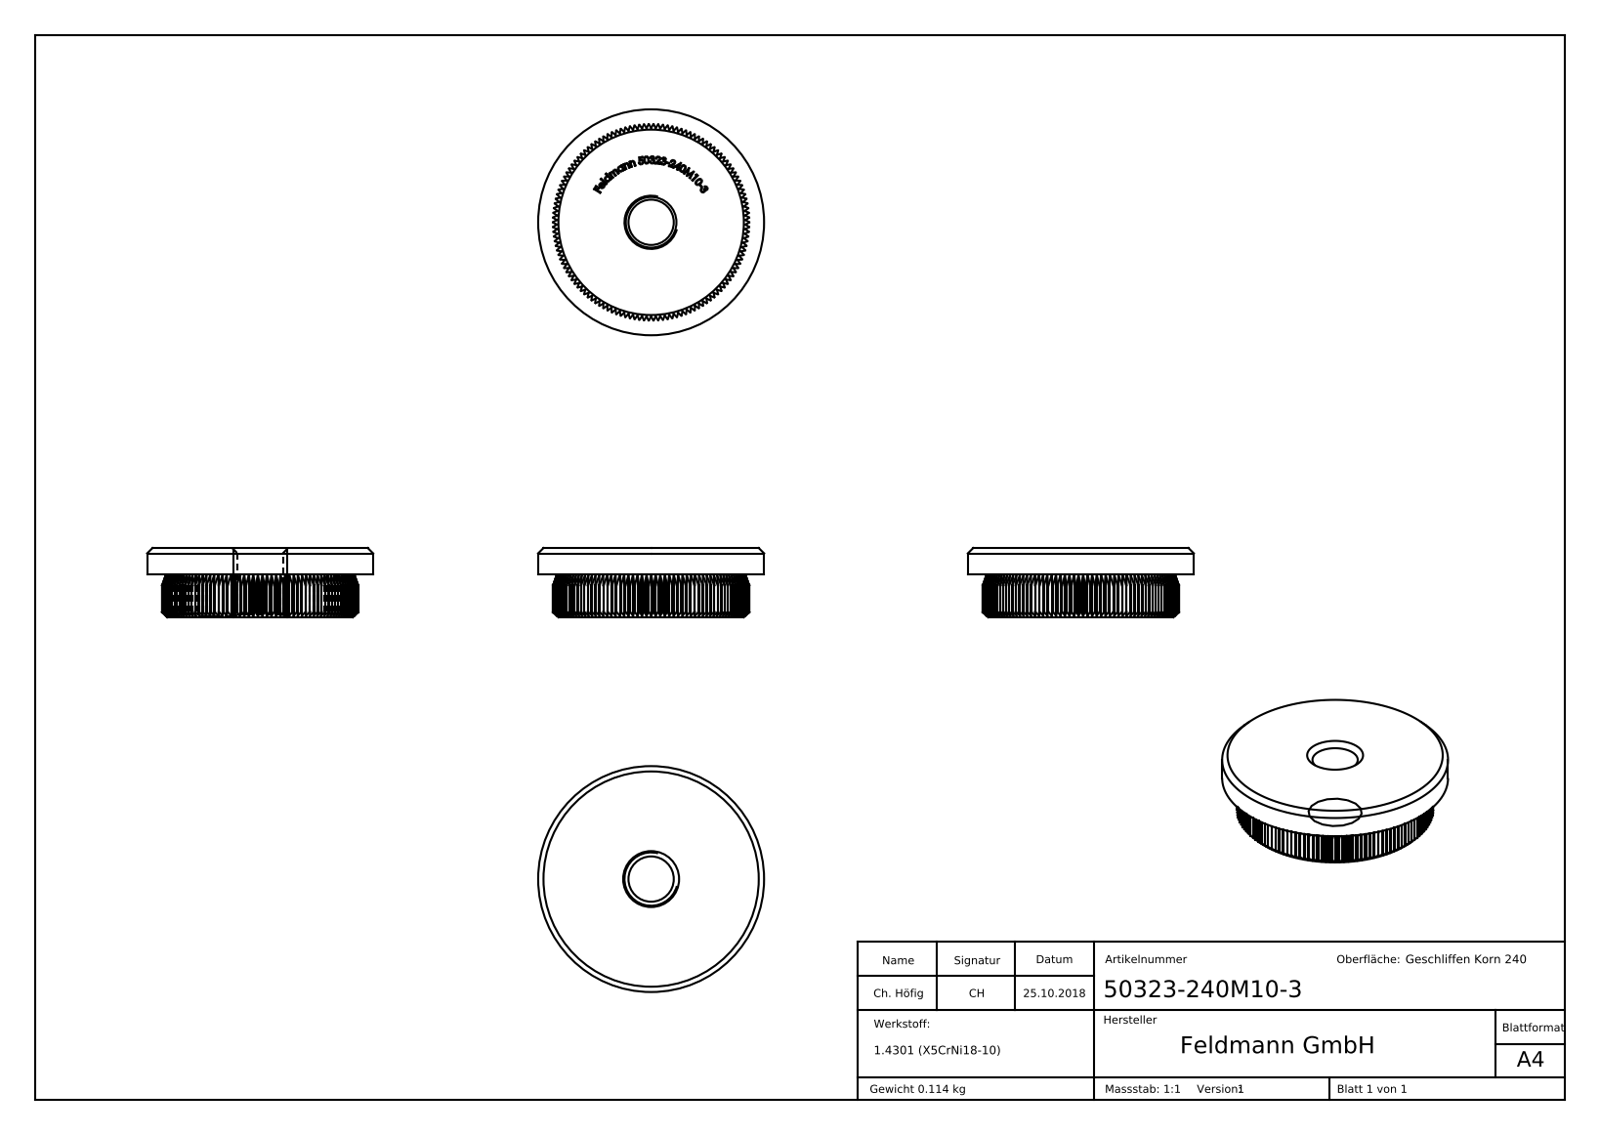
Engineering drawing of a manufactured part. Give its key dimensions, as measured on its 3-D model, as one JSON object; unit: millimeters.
{"part_name": "50323-240M10-3", "step_written_by": "SolidWorks 2015 (CONFIG_CONTROL_DESIGN)", "units": "millimeters", "bodies": {"solids": 1, "faces": 821, "planar": 410, "cylindrical": 134, "other": 277}, "overall_size": [42.4, 42.4, 13], "volume_mm3": 14394, "surface_area_mm2": 5221, "round_holes": [[8.5, 1]], "round_bosses_or_shafts": [[42.4, 1]], "partial_cylinders_radius": [[18.4, 1]], "face_to_face_distances": [13, 17.7, 8, 5, 17.72, 17.68, 7.9, 12.9, 0.54, 0.67]}
